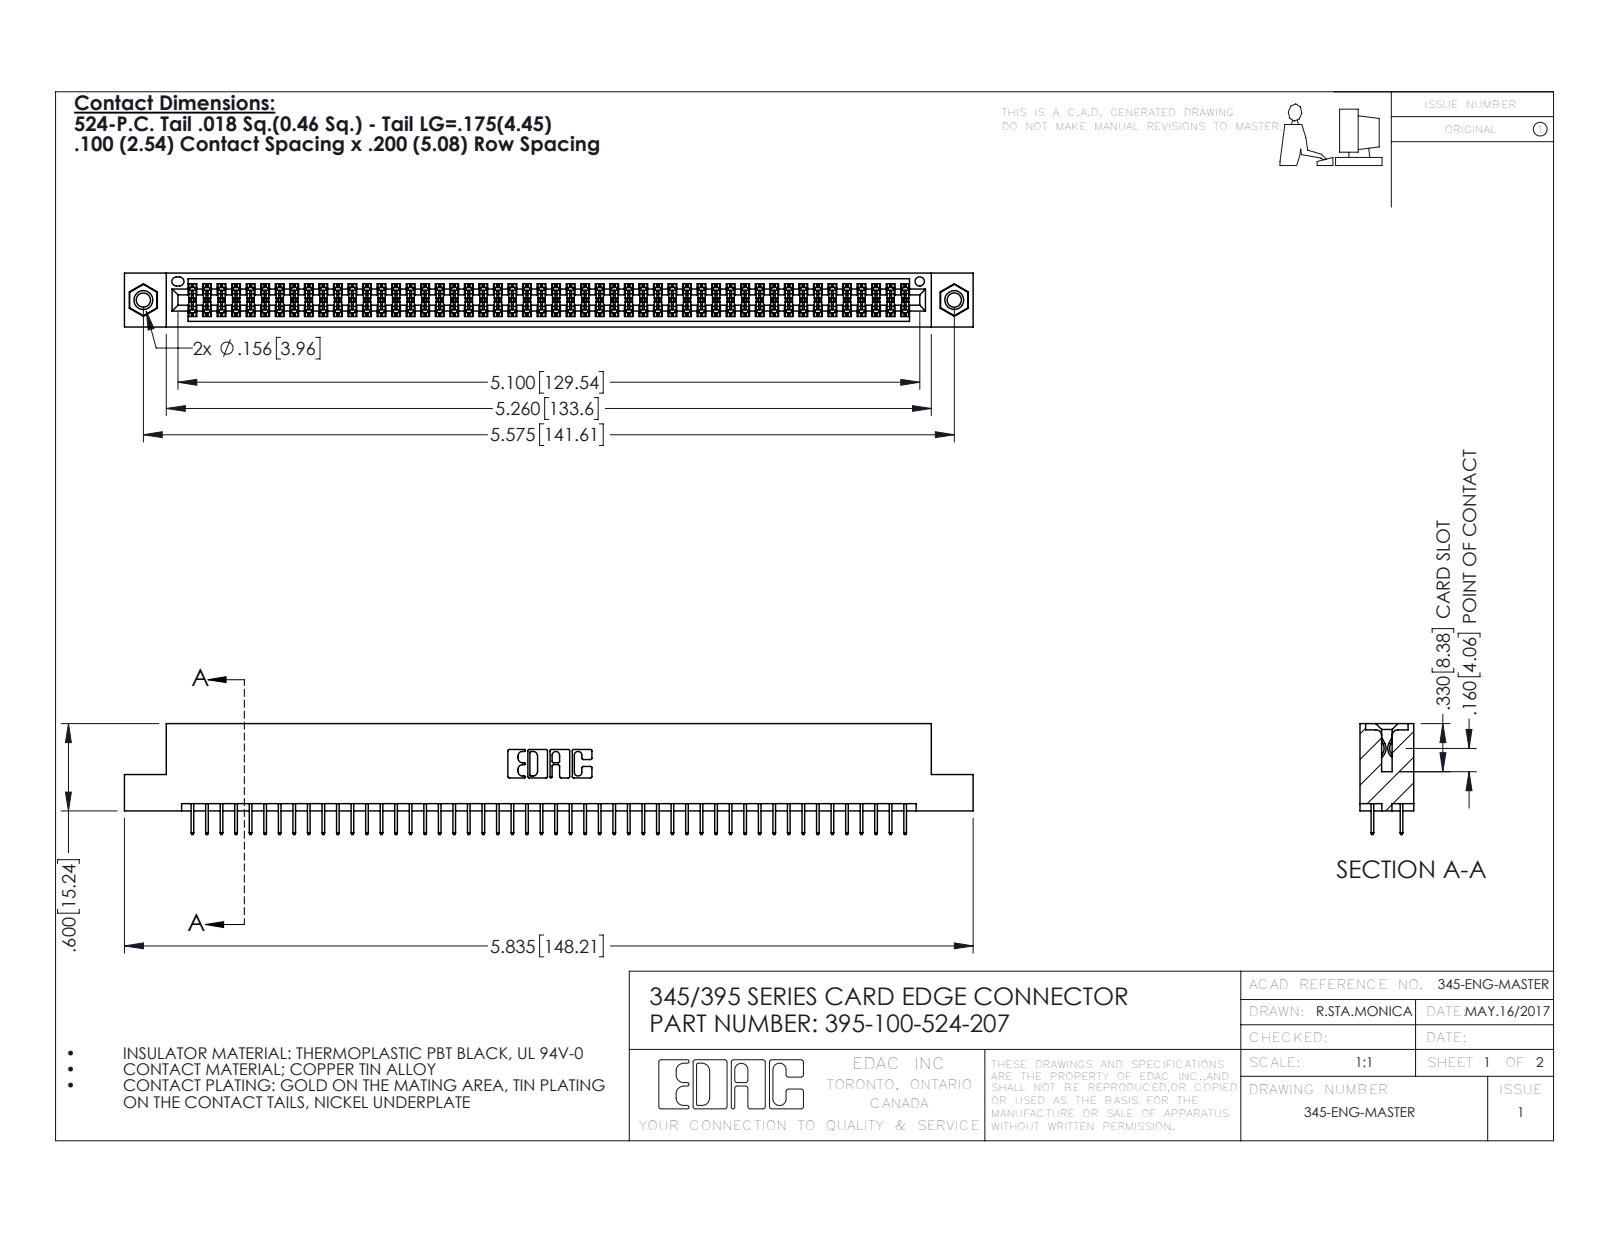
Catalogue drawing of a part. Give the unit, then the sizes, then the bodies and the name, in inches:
Units: inches
Overall size (bounding box): 5.835 × 0.762 × 0.37
Round holes (diameter × count): ⌀0.098 ×2, ⌀0.125 ×2, ⌀0.156 ×2, ⌀0.064 ×1
Round bosses / shafts (diameter × count): ⌀0.155 ×2
Partial cylindrical surfaces — rounded edges, fillets, slot ends (radius × count): R0.006 ×150, R0.01 ×22, R0.007 ×6, R0.031 ×6, R0.026 ×3, R0.014 ×2, R0.019 ×2, R0.022 ×2
Main face-to-face distances: 0.072, 0.298, 0.2, 0.37, 0.098, 0.272, 0.025, 0.225, 0.072, 0.175
Hole centre spacings: 0.27, 5.339, 5.575
Volume: 0.873 in³ · Surface area: 32.44 in²
Bodies: 103 solids, 5586 faces (4012 planar, 1558 cylindrical, 16 other)
Part name (STEP PRODUCT): 345-250-001_345-250-005-103; 395-100-524-207; 345 Part_Flush Mounting Lugs - 0.156 Dia-TI; 345-292-001_345-293-124
STEP written by: SolidWorks 2016 (CONFIG_CONTROL_DESIGN)
